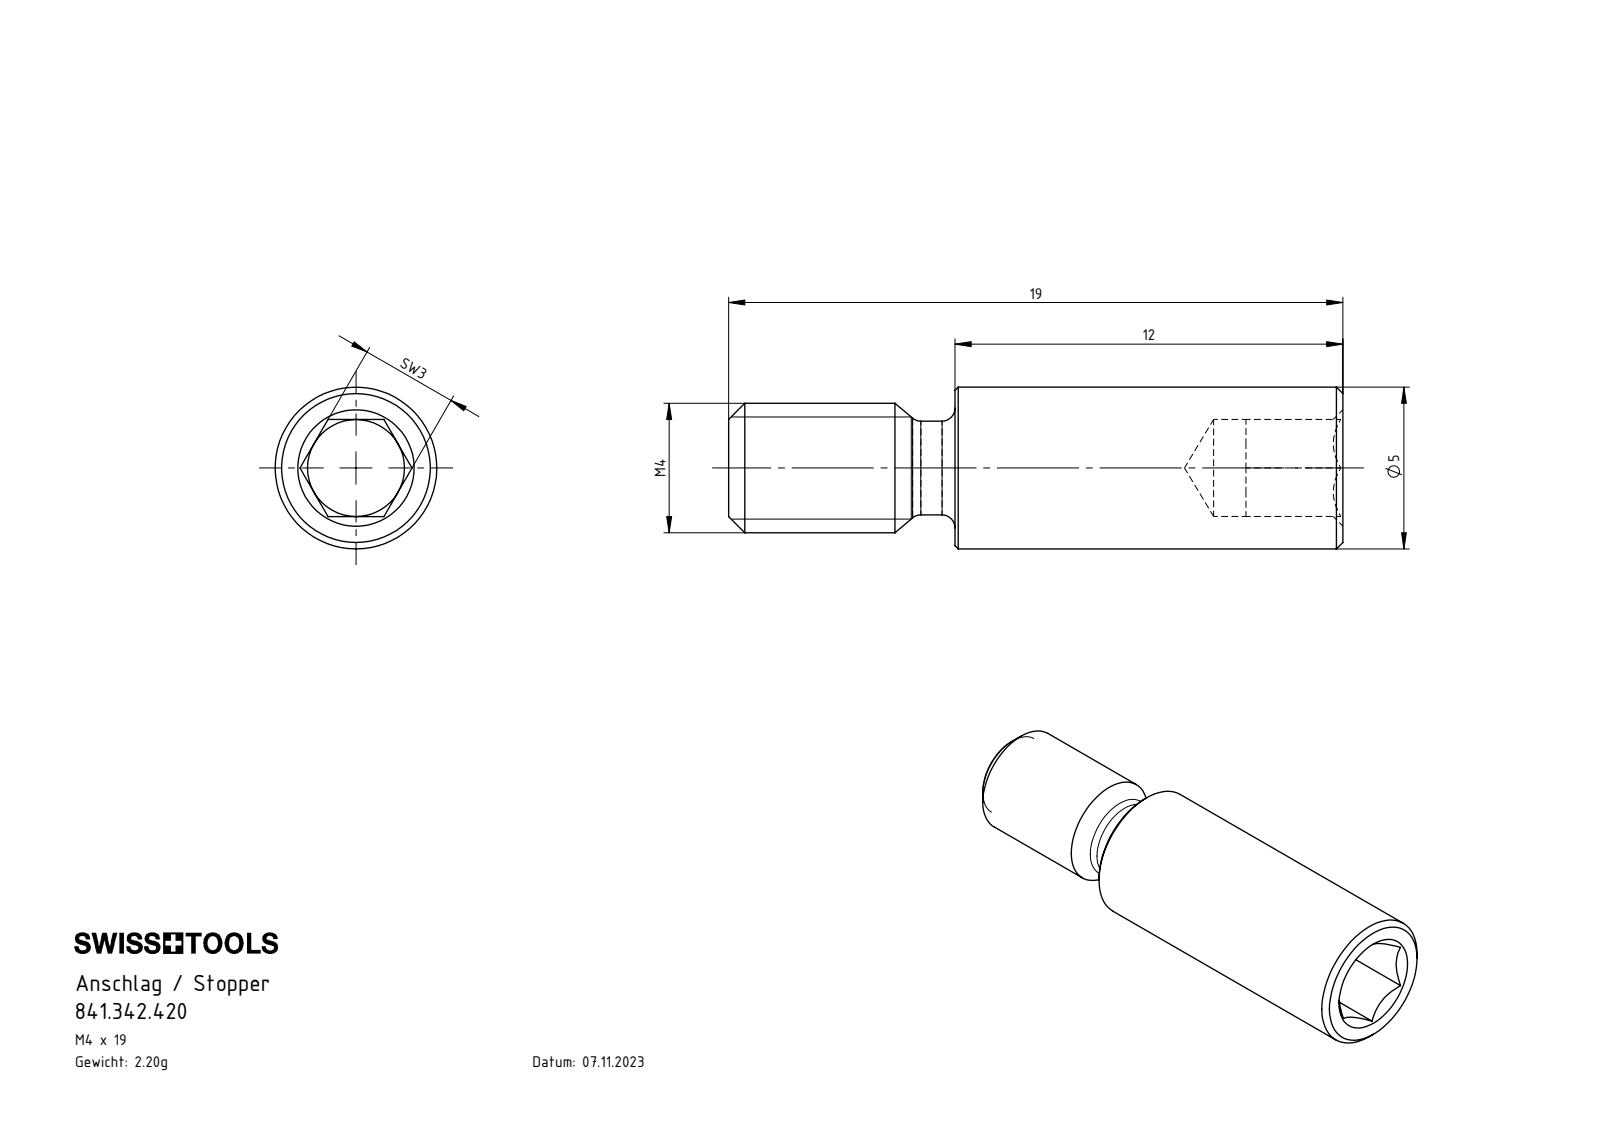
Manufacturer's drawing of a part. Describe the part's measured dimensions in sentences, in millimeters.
The part is named "841.342.420". Its 3-D file was written by "SolidWorks 2022 (AUTOMOTIVE_DESIGN)". It is 1 solid with 39 faces: 15 planar, 8 cylindrical and 16 other. Overall it measures 19 by 5 by 5 millimeters. Its volume is 280 cubic millimeters and its surface area 351 square millimeters. Round holes: 1 of diameter 3. Round bosses or shafts: 1 of diameter 5, 1 of diameter 4, 1 of diameter 2.9. The main face-to-face distances are 3, 7, 19, 12, 16, 9.
